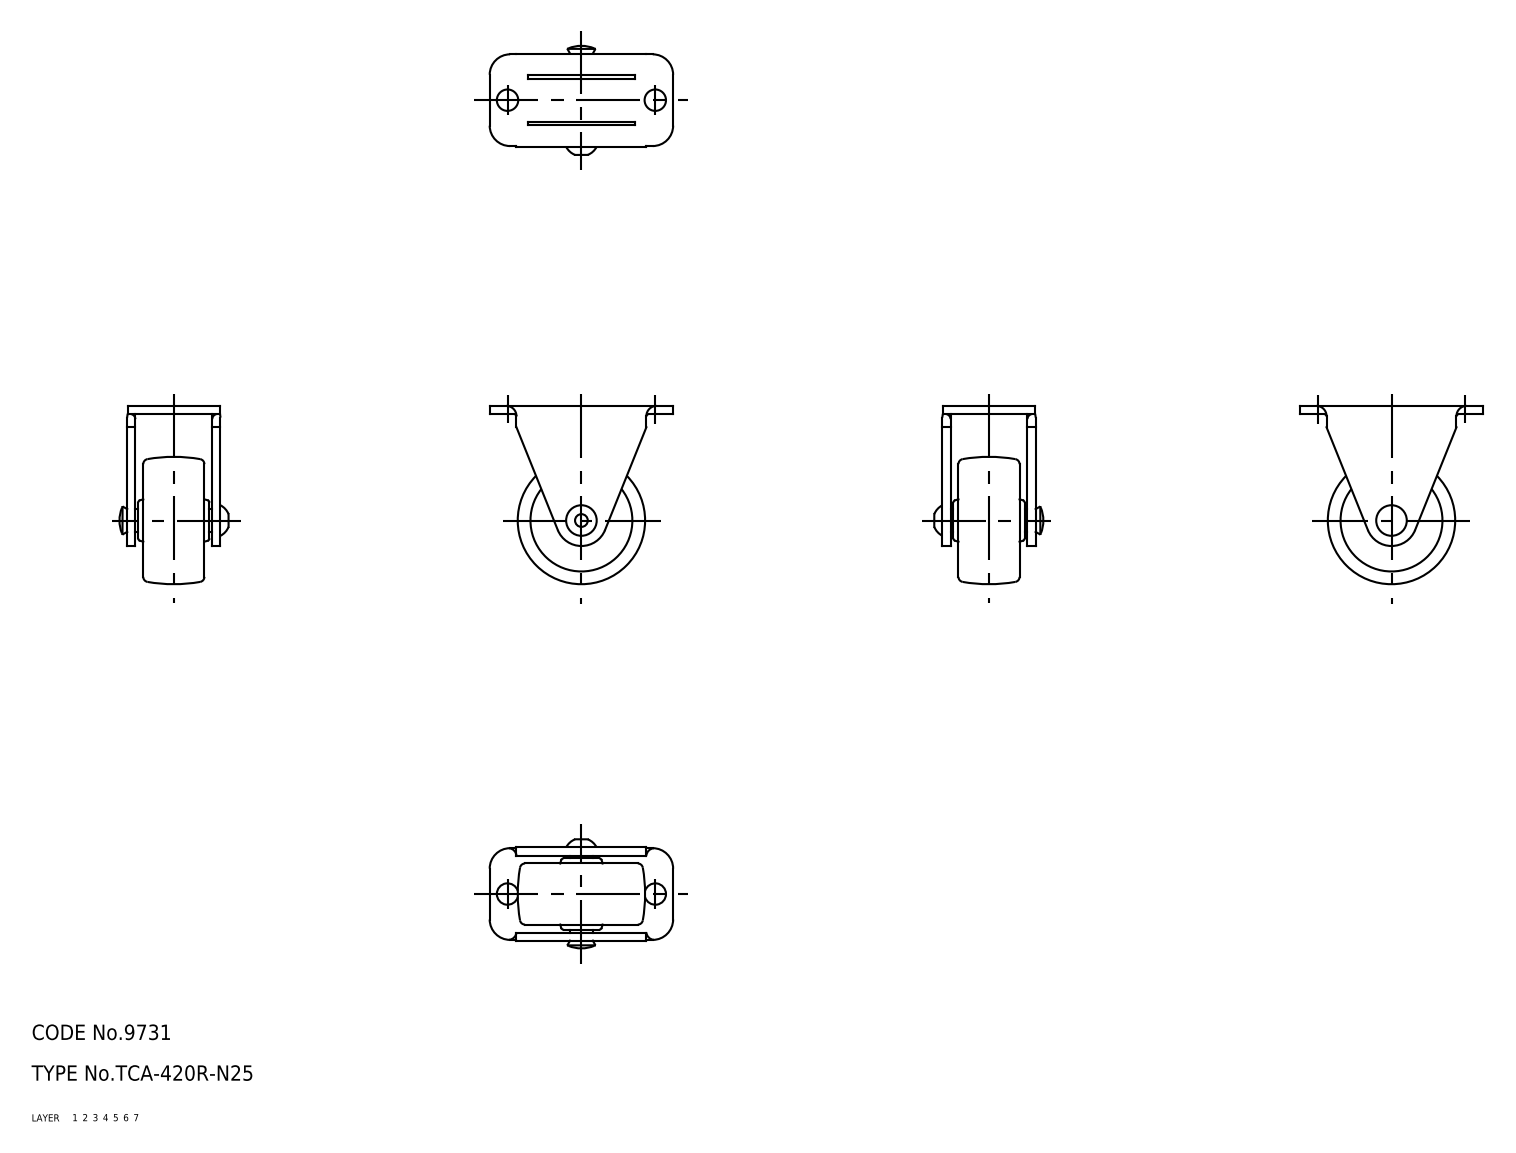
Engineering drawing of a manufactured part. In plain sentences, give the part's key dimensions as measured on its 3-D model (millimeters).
The part is named "wheel; axle; No_420_R_N25_1_178_36". Its 3-D file was written by "CADfix (AUTOMOTIVE_DESIGN)". It is 3 solids with 122 faces: 0 planar, 0 cylindrical and 122 other. Overall it measures 36 by 35 by 21.41 millimeters. Its volume is 6 949 cubic millimeters and its surface area 5 912 square millimeters.
